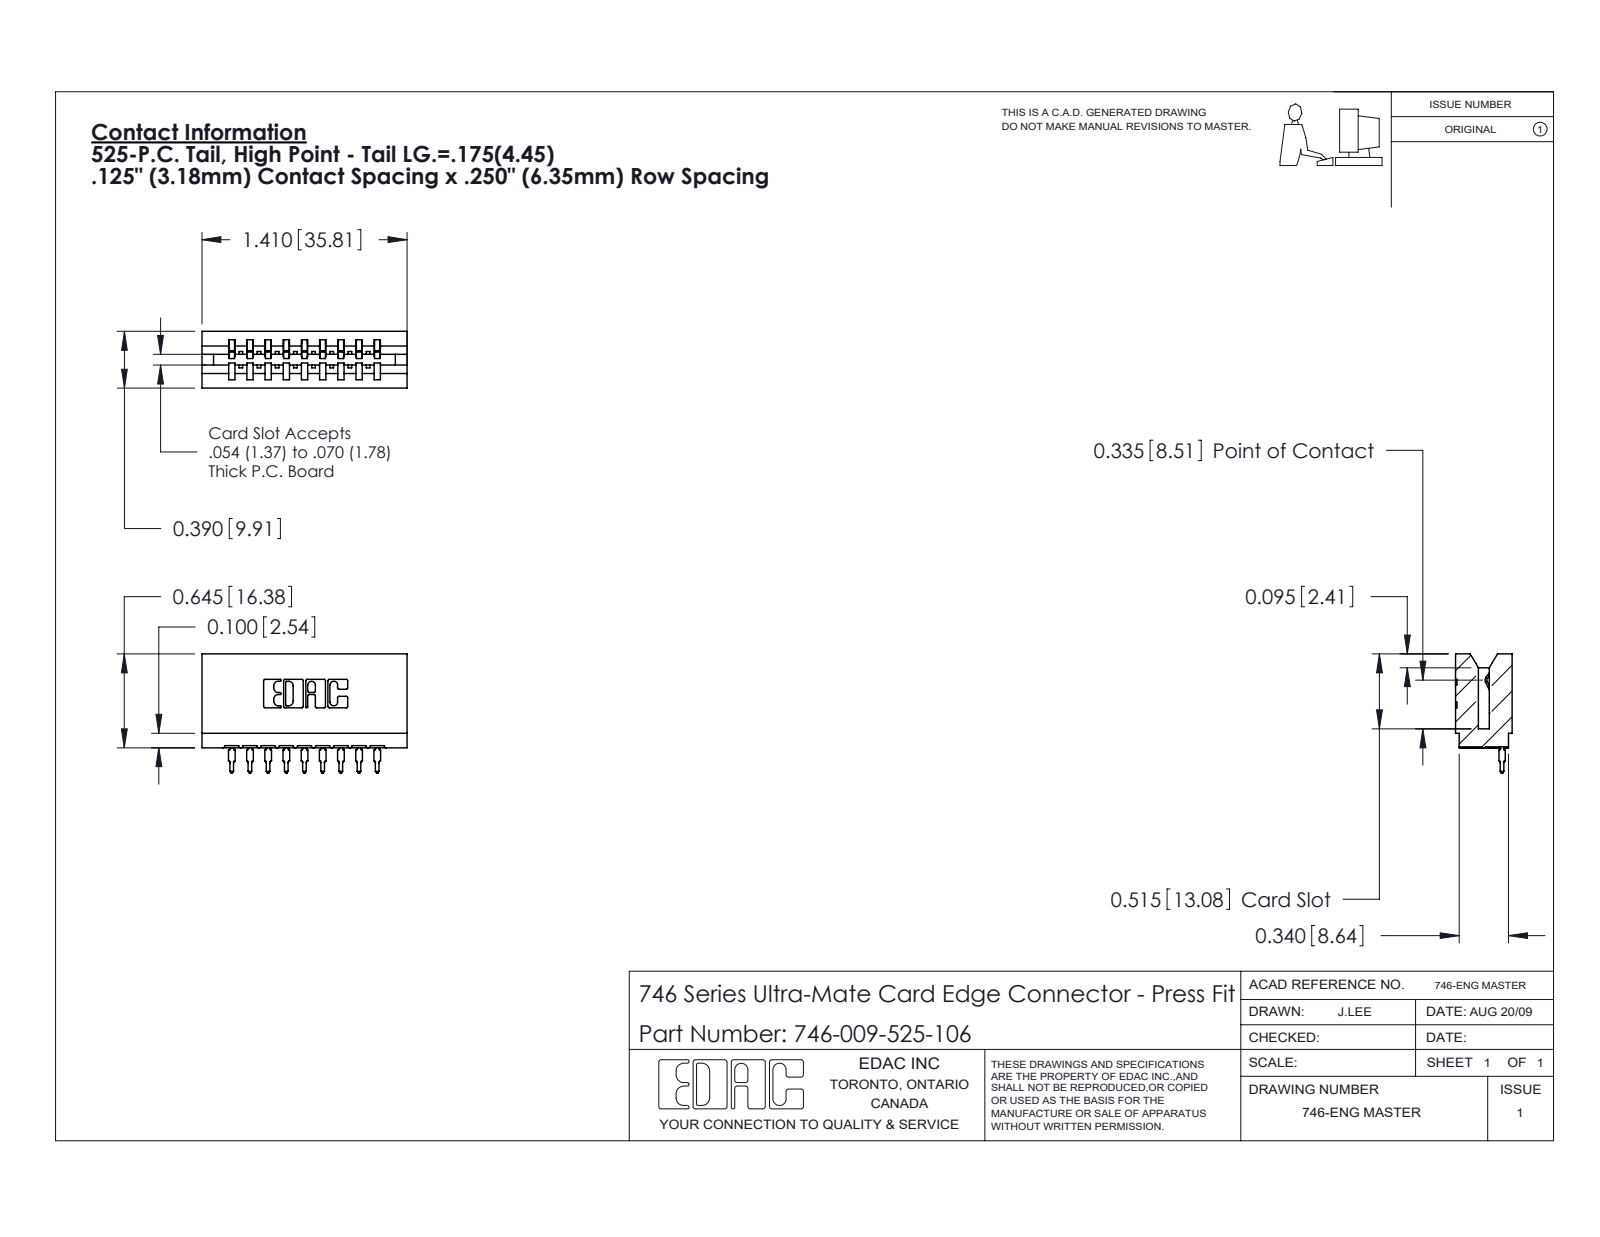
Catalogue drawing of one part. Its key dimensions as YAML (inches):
part_name: "746-009-525-106; 746-292-001_525; 746 Part_.515 Slot Depth - 06"
step_written_by: "SolidWorks 2020 (CONFIG_CONTROL_DESIGN)"
units: inches
bodies: {solids: 10, faces: 1070, planar: 623, cylindrical: 213, other: 234}
overall_size: [1.41, 0.819, 0.39]
volume: 0.24
surface_area: 8.132
partial_cylinders:
  - {radius: 0.01, count: 22}
  - {radius: 0.021, count: 18}
  - {radius: 0.015, count: 10}
  - {radius: 0.007, count: 6}
  - {radius: 0.031, count: 6}
  - {radius: 0.005, count: 4}
  - {radius: 0.011, count: 4}
  - {radius: 0.026, count: 3}
face_to_face_distances: [0.25, 0.5, 0.042, 0.333, 0.125, 0.125, 0.292, 0.208, 0.057, 0.75]
